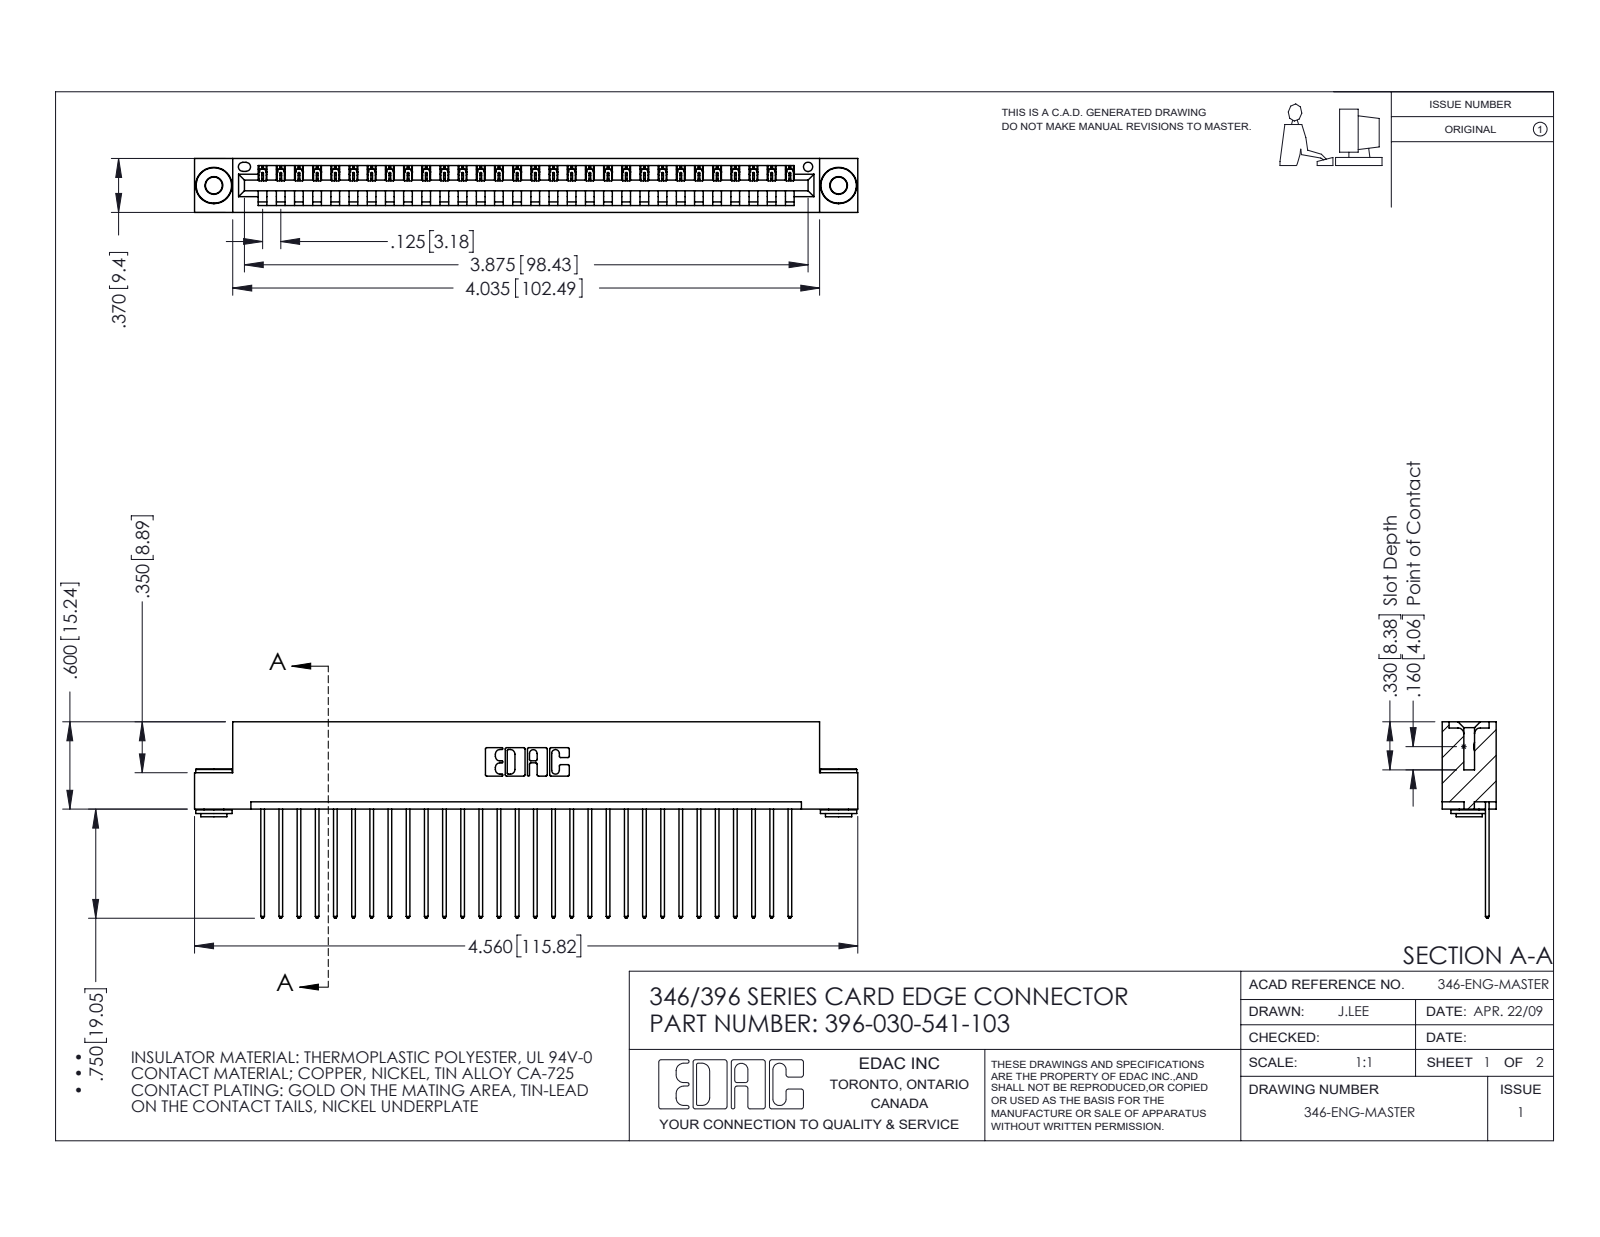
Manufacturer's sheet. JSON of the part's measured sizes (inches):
{"part_name": "396-030-541-103; 345-250-002_345-250-002-102; 345-292-001_345-293-141; 346 Part_Flush Mounting Lugs - 0.156 Dia-TH", "step_written_by": "SolidWorks 2016 (CONFIG_CONTROL_DESIGN)", "units": "inches", "bodies": {"solids": 33, "faces": 1900, "planar": 1286, "cylindrical": 606, "other": 8}, "overall_size": [4.56, 1.35, 0.37], "volume_in3": 0.679, "surface_area_in2": 22.6, "round_holes": [[0.116, 2], [0.156, 2], [0.064, 1]], "round_bosses_or_shafts": [[0.25, 2], [0.18, 2], [0.136, 2]], "partial_cylinders_radius": [[0.006, 60], [0.01, 60], [0.01, 22], [0.007, 6], [0.031, 6], [0.026, 3], [0.031, 2], [0.04, 2]], "face_to_face_distances": [0.048, 0.322, 0.25, 0.37, 0.025, 0.072, 0.298, 0.148, 0.222, 0.1], "hole_center_spacings": [0.246, 4.087, 4.295]}
